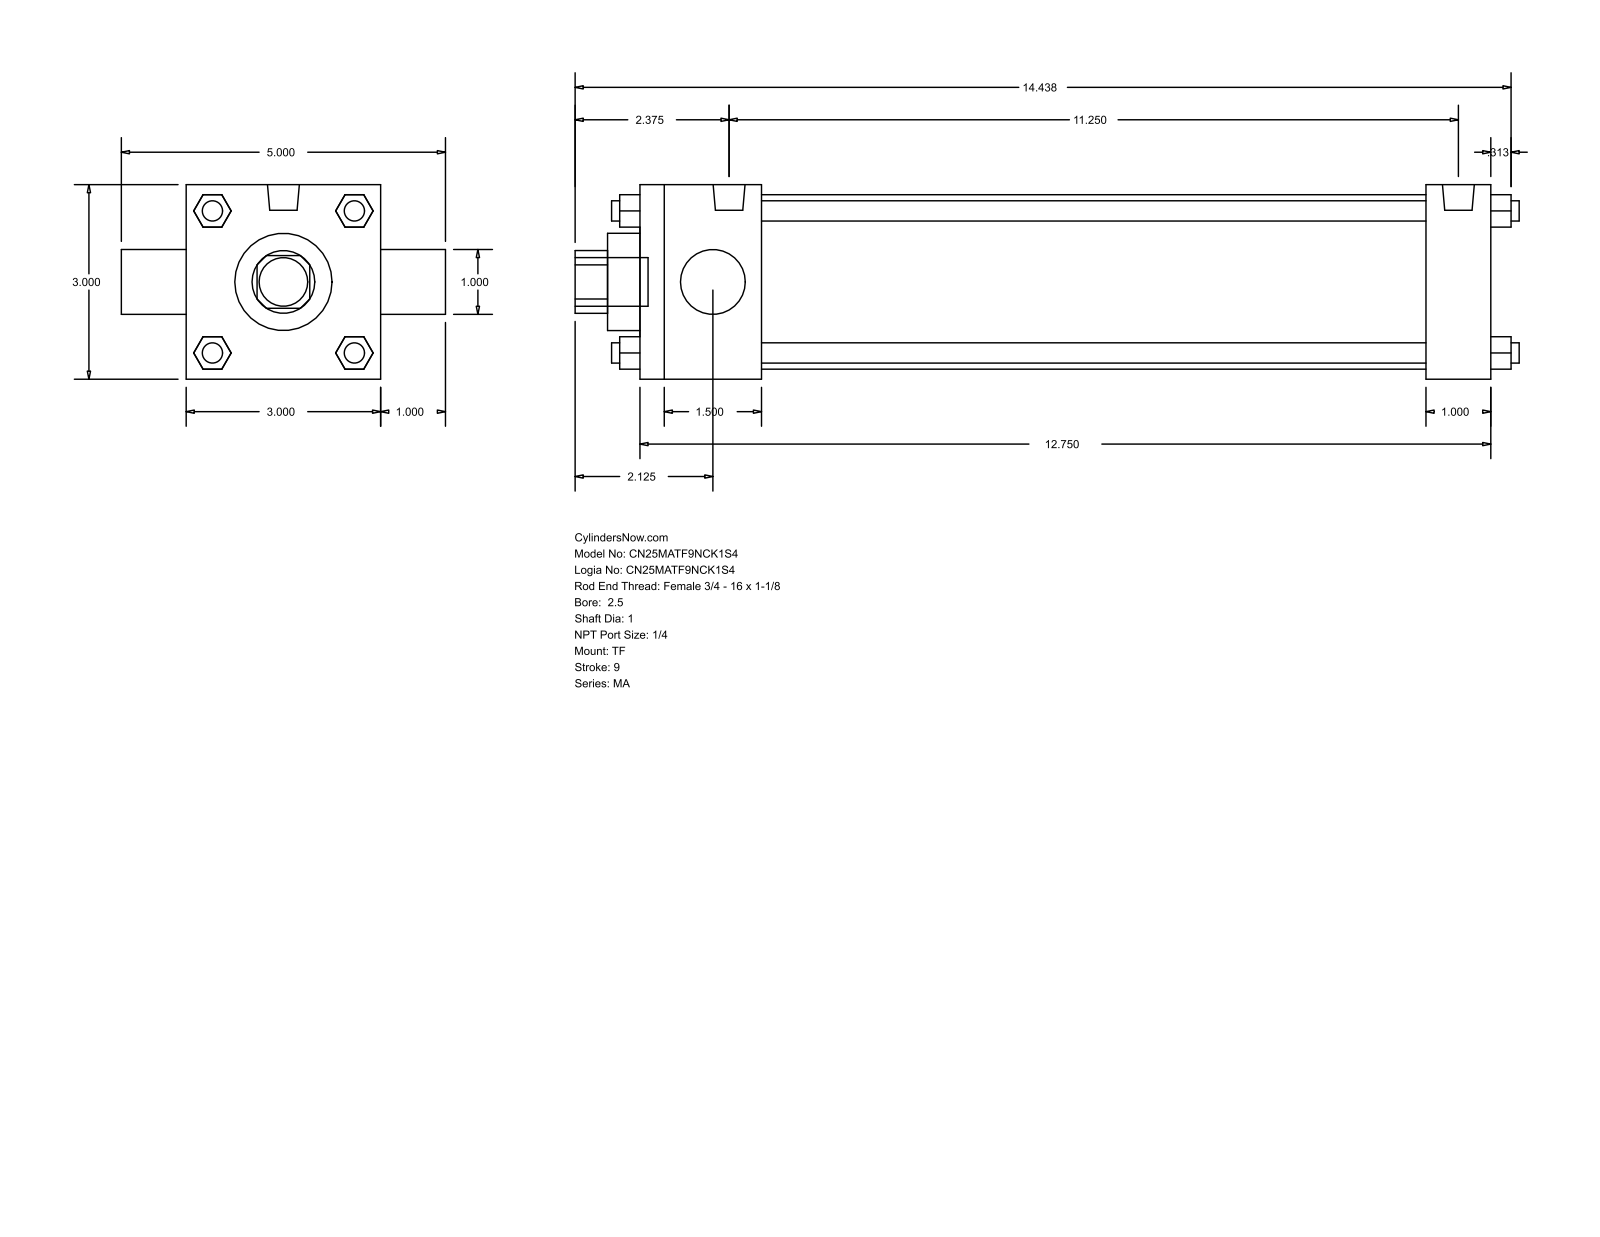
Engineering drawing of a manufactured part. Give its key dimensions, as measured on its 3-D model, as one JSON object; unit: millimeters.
{"part_name": "MA_TF__0250_1", "step_written_by": "GSSL Pune (CONFIG_CONTROL_DESIGN)", "units": "millimeters", "bodies": {"solids": 0, "faces": 120, "planar": 92, "cylindrical": 28, "other": 0}, "overall_size": [369.89, 127, 76.2], "round_holes": [[25.4, 2], [38.1, 1], [68.33, 1]], "round_bosses_or_shafts": [[7.94, 7], [12.49, 2], [19.05, 1]], "partial_cylinders_radius": [[12.29, 1]], "face_to_face_distances": [76.2, 333.37, 12.7, 47.63, 307.98, 260.35, 285.74, 25.39, 25.4, 101.6]}
